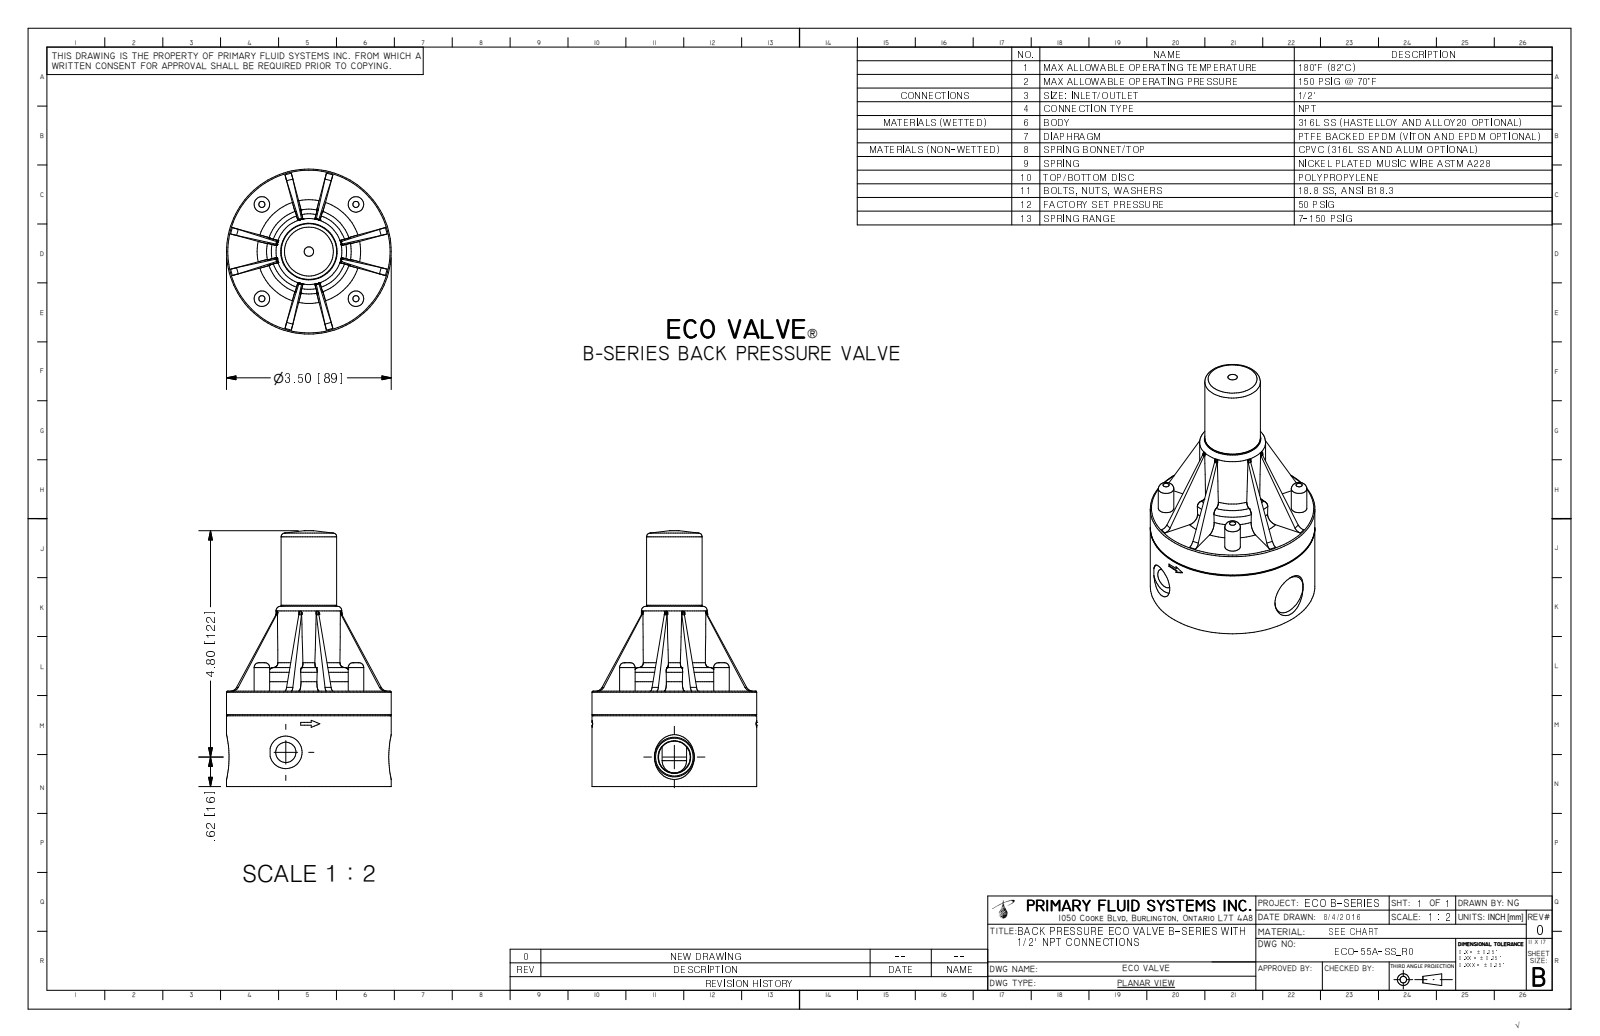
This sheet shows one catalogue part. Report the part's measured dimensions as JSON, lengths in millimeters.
{"part_name": "ECO-55A-SS_R0", "step_written_by": "Autodesk Inventor 2009 (AUTOMOTIVE_DESIGN)", "units": "millimeters", "bodies": {"solids": 1, "faces": 167, "planar": 70, "cylindrical": 39, "other": 58}, "overall_size": [137.8, 88.9, 88.9], "volume_mm3": 398200, "surface_area_mm2": 50070, "round_holes": [[5.8, 2], [6.5, 2], [6.5, 2], [10.2, 2], [10.9, 2], [17.6, 2]], "round_bosses_or_shafts": [[8.4, 4], [88.9, 1], [45.7, 1], [35.6, 1], [30, 1]], "partial_cylinders_radius": [[3.8, 8], [43.9, 1]], "face_to_face_distances": [51.4, 54.6, 6.9, 38.1, 13.3, 78.4, 34.3, 59.1, 31.2, 44.6], "hole_center_spacings": [71.8]}
